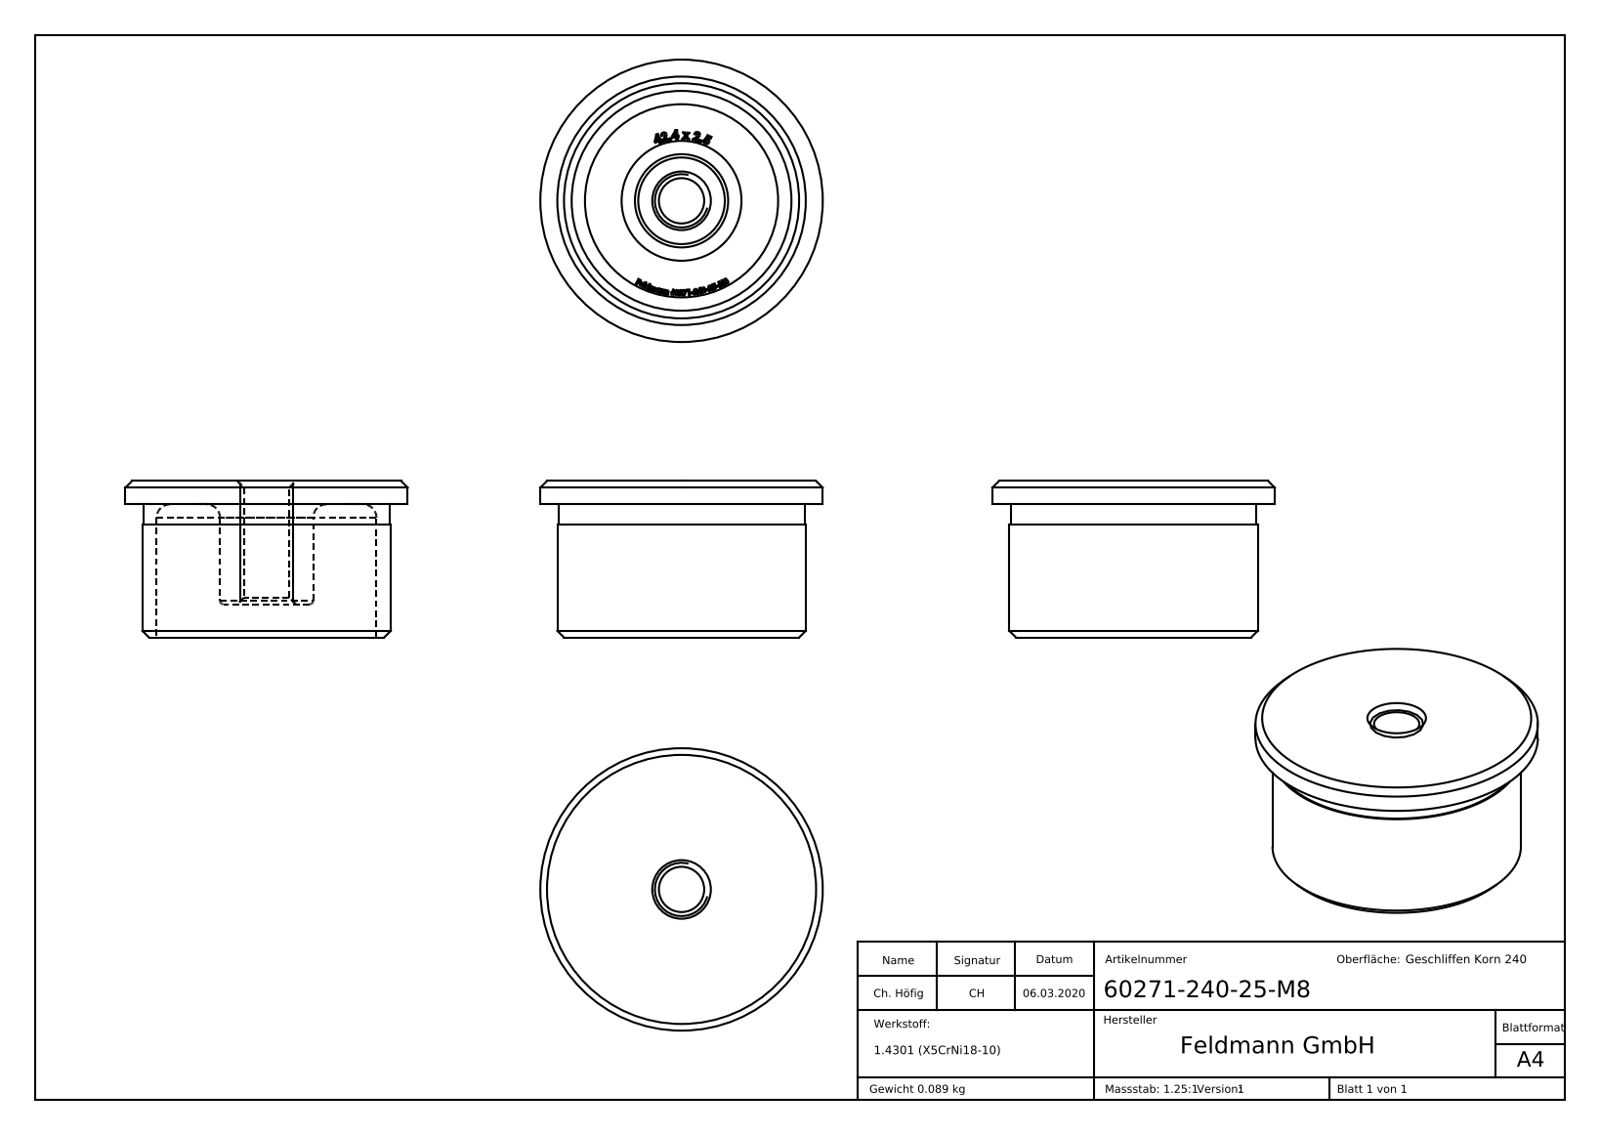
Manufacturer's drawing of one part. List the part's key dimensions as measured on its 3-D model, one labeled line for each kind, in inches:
Part name (STEP PRODUCT): 60271-240-25-M8
STEP written by: SolidWorks 2015 (CONFIG_CONTROL_DESIGN)
Units: inches
Bodies: 1 solid, 403 faces (255 planar, 6 cylindrical, 142 other)
Overall size (bounding box): 1.669 × 1.669 × 0.925
Volume: 0.686 in³ · Surface area: 13.07 in²
Round holes (diameter × count): ⌀0.268 ×1, ⌀1.299 ×1
Round bosses / shafts (diameter × count): ⌀1.669 ×1, ⌀1.469 ×1, ⌀1.453 ×1, ⌀0.551 ×1
Main face-to-face distances: 0.138, 0.787, 0.925, 0.197, 0.591, 0.728, 0.669, 0.472, 0.118, 0.256
